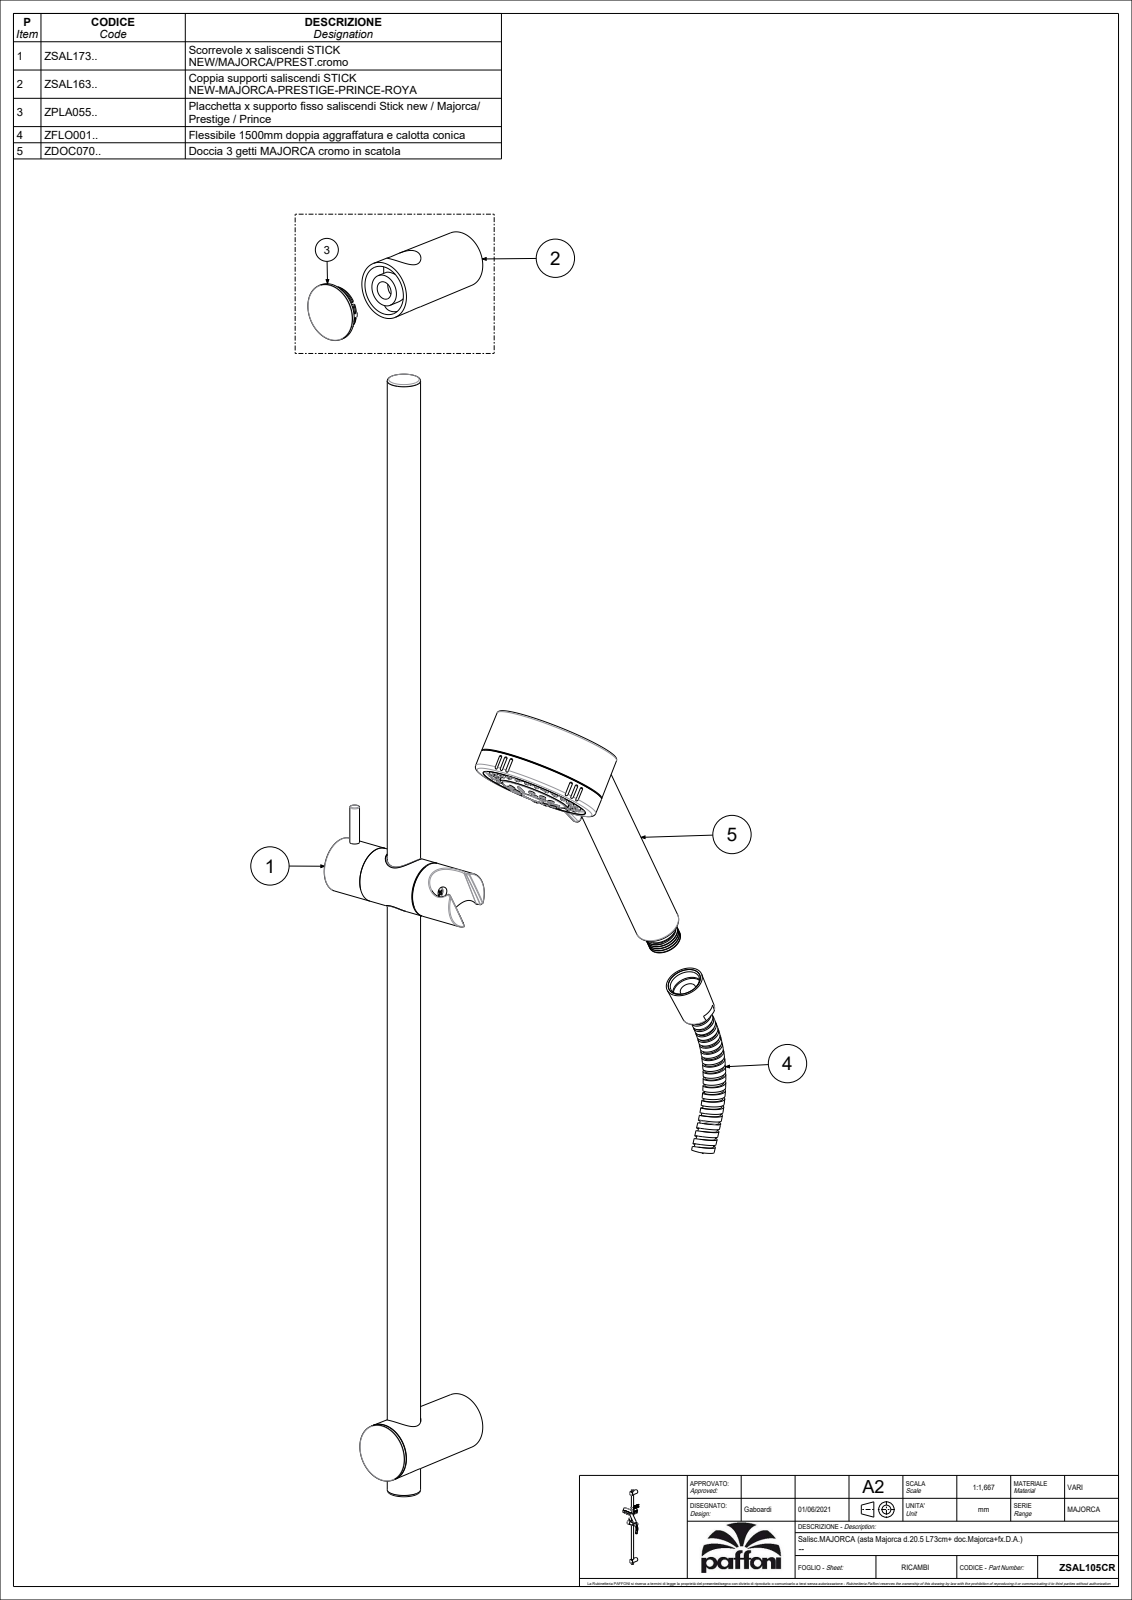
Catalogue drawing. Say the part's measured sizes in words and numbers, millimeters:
The part is named "ZSAL105CR". Its 3-D file was written by "CREO PARAMETRIC BY PTC INC, 2020044 (CONFIG_CONTROL_DESIGN)". It is 7 solids with 2051 faces: 477 planar, 581 cylindrical and 993 other. Overall it measures 734 by 220.01 by 132.17 millimeters. Its volume is 511 016 cubic millimeters and its surface area 228 075 square millimeters. Round holes: 63 of diameter 2.5, 6 of diameter 3, 3 of diameter 31, 2 of diameter 5.4, 2 of diameter 11, 2 of diameter 11.2, 2 of diameter 14, 2 of diameter 15.3, 2 of diameter 22.5, 1 of diameter 3.4, 1 of diameter 3.8, 1 of diameter 8. Round bosses or shafts: 16 of diameter 4, 2 of diameter 36.5, 2 of diameter 35, 2 of diameter 22.4, 2 of diameter 12, 1 of diameter 79.14, 1 of diameter 75.94, 1 of diameter 57. Partial cylindrical surfaces (rounded edges, fillets, slot ends): 60 of radius 0.1, 15 of radius 1.24, 15 of radius 2.05, 9 of radius 1.5, 8 of radius 0.6, 6 of radius 0.5, 6 of radius 1, 5 of radius 0.3. The main face-to-face distances are 1.1, 366.51, 1.5, 367.61, 365.41, 4.4, 8.52, 4.12, 2, 6.01. The hole center spacings are 15, 13.5, 10.3, 13.49, 25.98, 5.97, 20.78, 21.58.
